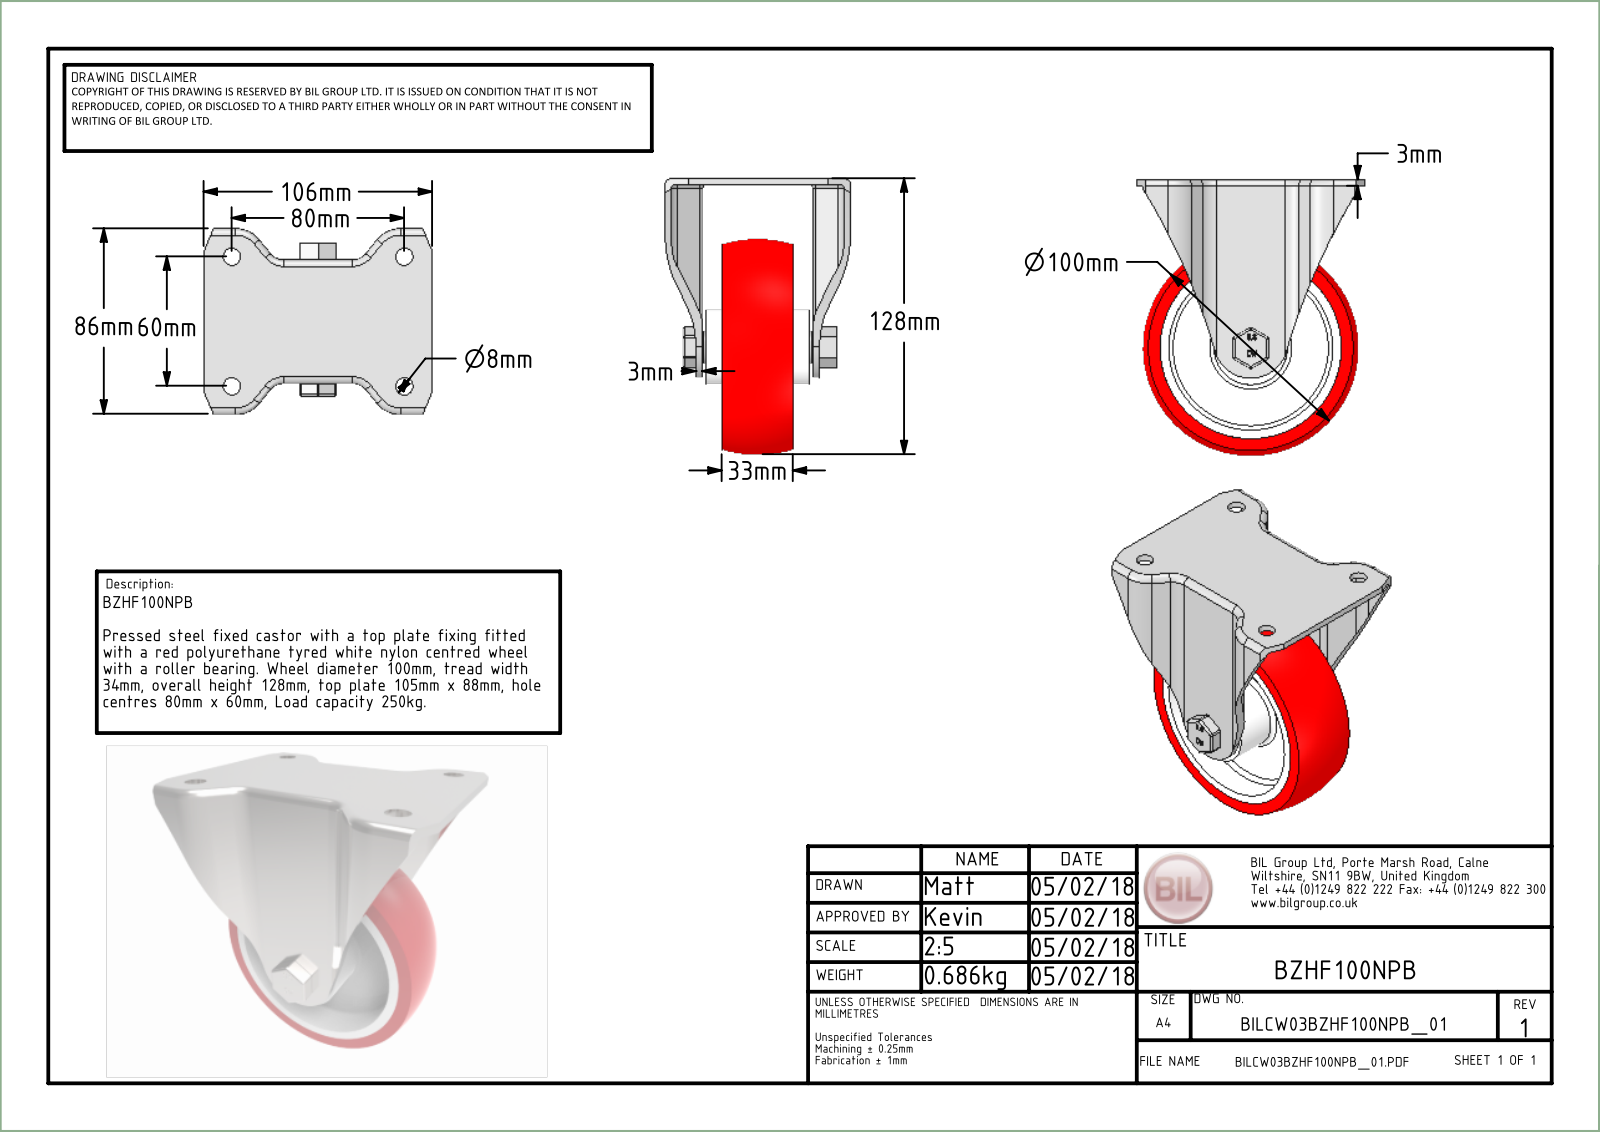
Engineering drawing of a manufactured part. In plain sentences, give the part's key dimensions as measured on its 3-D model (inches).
The part is named "BZHF100NPB v4; BZHF100AS v1; ZINC PLATED, PRESSED STEEL BRACKET; BZH100WNPRB61 v1 (+7 more)". Its 3-D file was written by "Autodesk Translation Framework v14.10.0.0 (AUTOMOTIVE_DESIGN)". It is 17 solids with 455 faces: 206 planar, 161 cylindrical and 88 other. Overall it measures 5.039 by 4.173 by 3.465 inches. Its volume is 14.09 cubic inches and its surface area 176.6 square inches. Round holes: 1 of diameter 0.394, 1 of diameter 0.404, 1 of diameter 0.413, 1 of diameter 0.472, 1 of diameter 0.591, 1 of diameter 0.61, 1 of diameter 0.925, 1 of diameter 1.063, 1 of diameter 3.189. Round bosses or shafts: 8 of diameter 0.157, 1 of diameter 1.201, 1 of diameter 1.059, 1 of diameter 0.906, 1 of diameter 0.63, 1 of diameter 0.388, 1 of diameter 0.32. Partial cylindrical surfaces (rounded edges, fillets, slot ends): 18 of radius 0.02, 12 of radius 0.059, 10 of radius 0.118, 8 of radius 0.177, 6 of radius 0.03, 4 of radius 0.236, 4 of radius 0.315, 4 of radius 0.472. The main face-to-face distances are 0.118, 0.925, 0.591, 0.748, 0.335, 1.083, 1.673, 1.791, 0.453, 1.043.
